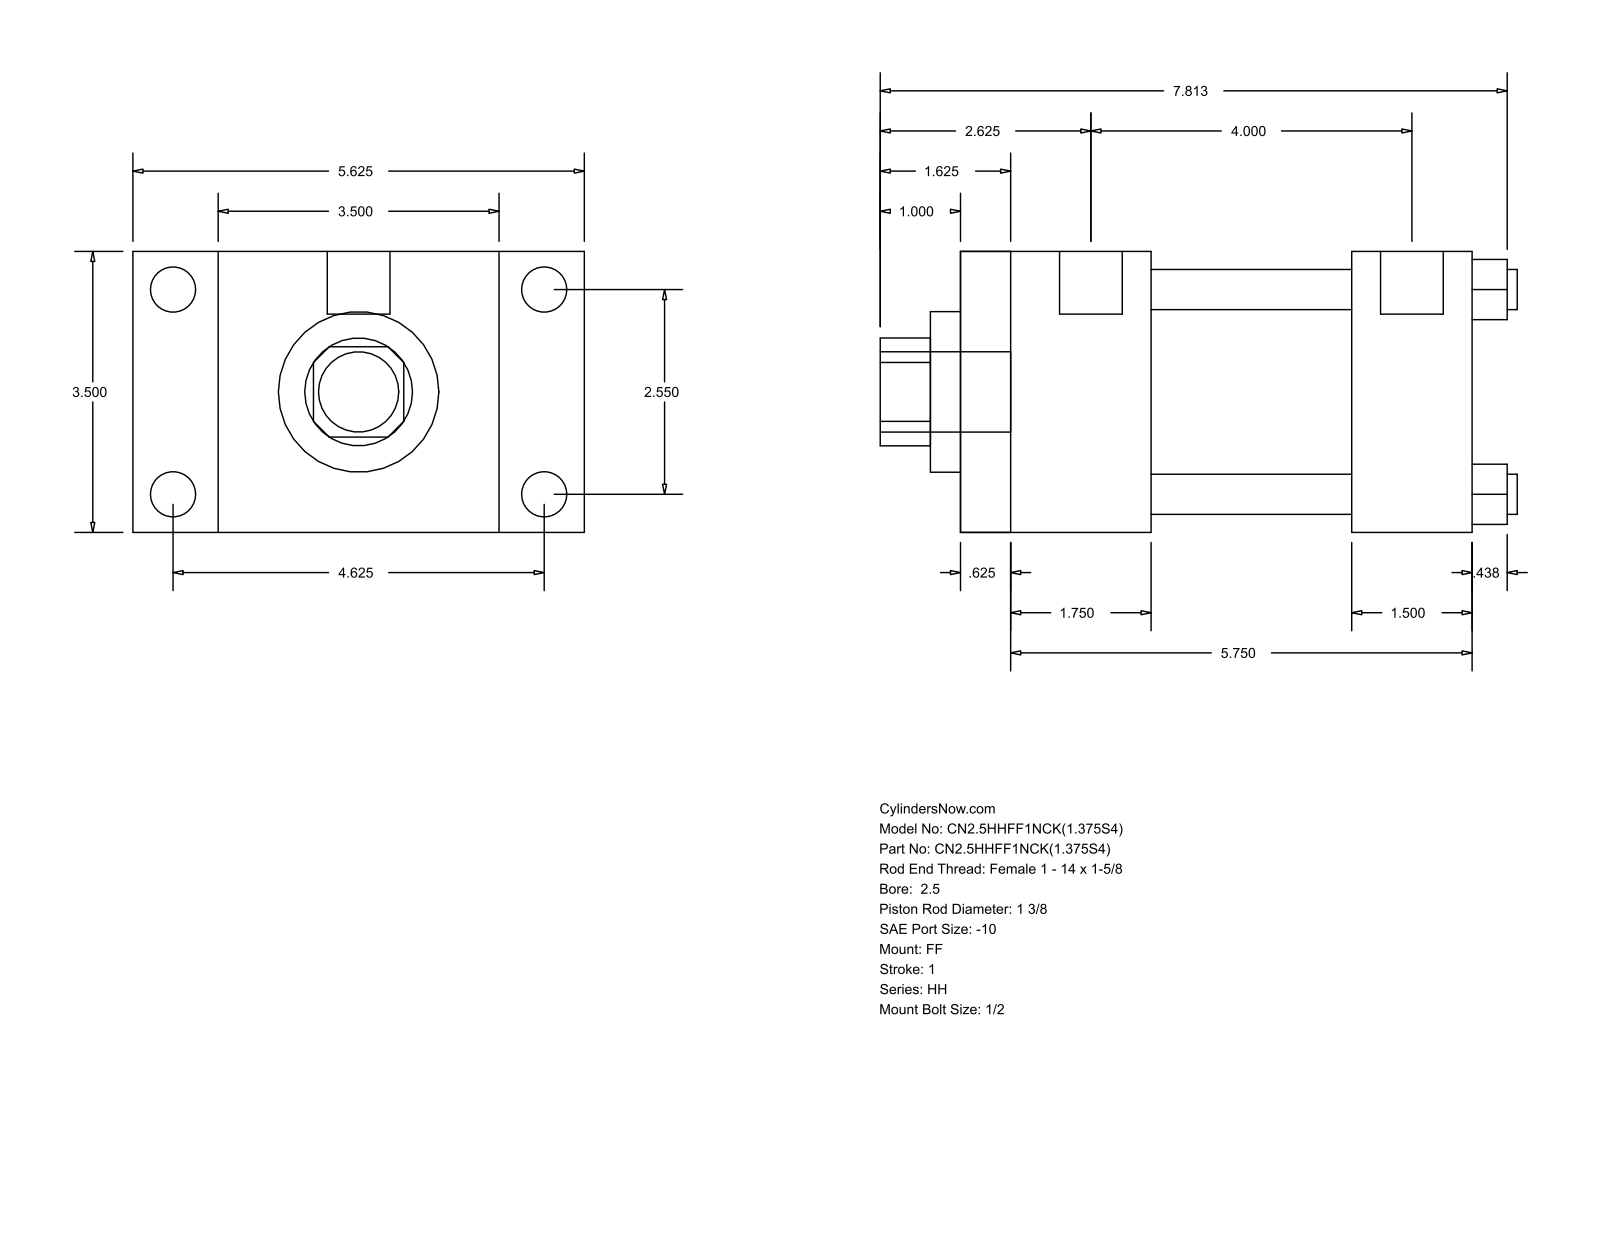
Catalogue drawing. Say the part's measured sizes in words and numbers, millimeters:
The part is named "HH_FF__0250_1.375". Its 3-D file was written by "GSSL Pune (CONFIG_CONTROL_DESIGN)". It is 0 solids with 92 faces: 64 planar, 28 cylindrical and 0 other. Overall it measures 201.61 by 142.88 by 88.9 millimeters. Round holes: 4 of diameter 12.7, 1 of diameter 34.92, 1 of diameter 50.8, 1 of diameter 73.03. Round bosses or shafts: 4 of diameter 14.3, 4 of diameter 5.56, 2 of diameter 19.84, 1 of diameter 25.4. Partial cylindrical surfaces (rounded edges, fillets, slot ends): 1 of radius 17.06. The main face-to-face distances are 88.9, 161.92, 15.87, 146.05, 115.89, 60.32, 44.45, 101.6, 123.82, 107.95. The hole center spacings are 45.79, 64.76, 91.58.
